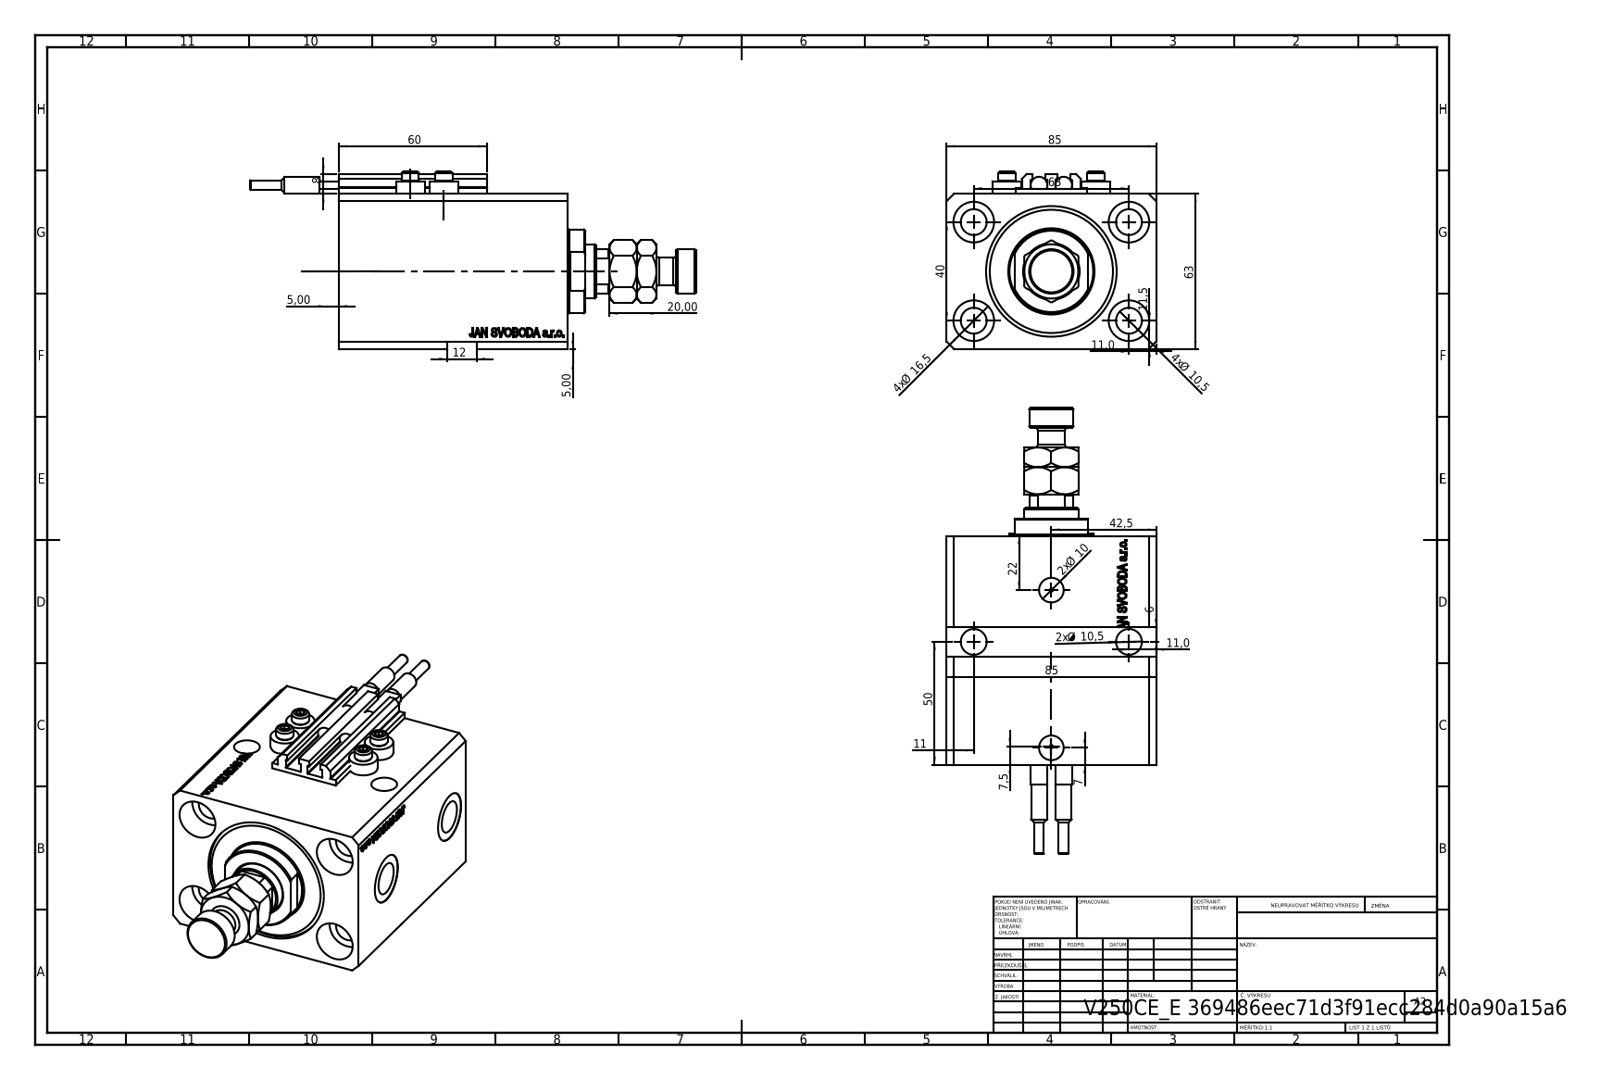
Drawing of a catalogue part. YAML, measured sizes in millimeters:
part_name: "V250CE_VC_E; ALLEN BOLT V250CE; SWITCH_V250CE; V250CE_C_VCP (+2 more)"
step_written_by: "SolidWorks 2019 (CONFIG_CONTROL_DESIGN)"
units: millimeters
bodies: {solids: 11, faces: 1191, planar: 583, cylindrical: 142, other: 466}
overall_size: [180.9, 85, 72]
volume: 451492
surface_area: 103930
round_holes:
  - {diameter: 10.5, count: 6}
  - {diameter: 1.25, count: 4}
  - {diameter: 4, count: 4}
  - {diameter: 16.5, count: 4}
  - {diameter: 10, count: 2}
  - {diameter: 13.16, count: 2}
  - {diameter: 20, count: 2}
  - {diameter: 12.5, count: 1}
  - {diameter: 22, count: 1}
  - {diameter: 40, count: 1}
  - {diameter: 53, count: 1}
round_bosses_or_shafts:
  - {diameter: 11.6, count: 4}
  - {diameter: 7, count: 4}
  - {diameter: 6.8, count: 2}
  - {diameter: 6.5, count: 2}
  - {diameter: 4, count: 2}
  - {diameter: 34, count: 1}
  - {diameter: 18, count: 1}
  - {diameter: 11, count: 1}
partial_cylinders:
  - {radius: 0.2, count: 10}
  - {radius: 10.5, count: 1}
face_to_face_distances: [63, 85, 93, 65.9, 54.5, 27.1, 11.4, 81.6, 3, 65]
hole_center_spacings: [37.31, 63, 13.6, 15.4, 24.96, 28.02, 28.43, 33.62]
